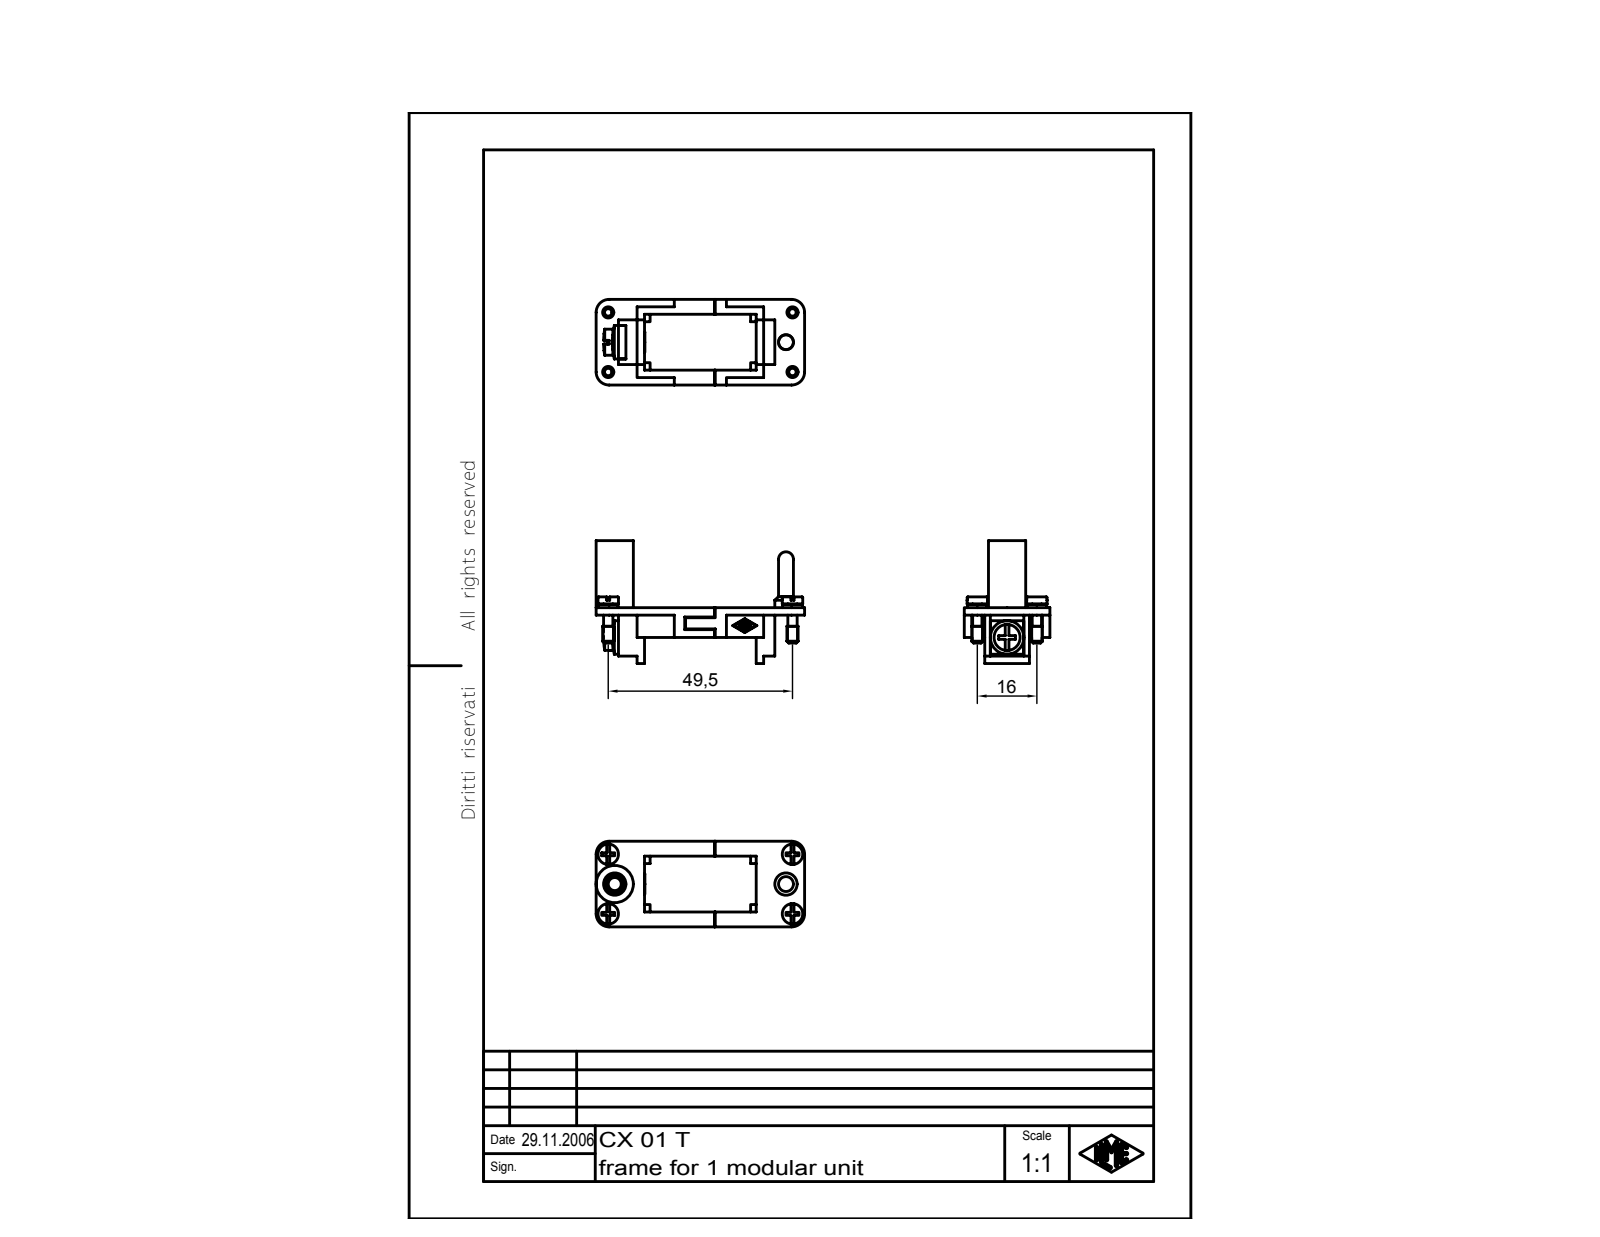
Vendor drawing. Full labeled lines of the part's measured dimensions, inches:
Part name (STEP PRODUCT): CX 01 T
STEP written by: Autodesk Inventor 7 (AUTOMOTIVE_DESIGN)
Units: inches
Bodies: 4 solids, 332 faces (182 planar, 62 cylindrical, 88 other)
Overall size (bounding box): 2.205 × 1.299 × 0.906
Volume: 0.388 in³ · Surface area: 10.89 in²
Round holes (diameter × count): ⌀0.157 ×2, ⌀0.138 ×1, ⌀0.236 ×1
Round bosses / shafts (diameter × count): ⌀0.217 ×2, ⌀0.209 ×2, ⌀0.157 ×2, ⌀0.118 ×2, ⌀0.098 ×2, ⌀0.394 ×1, ⌀0.354 ×1, ⌀0.276 ×1
Partial cylindrical surfaces — rounded edges, fillets, slot ends (radius × count): R0.004 ×14, R0.138 ×4
Main face-to-face distances: 0.079, 0.748, 0.197, 0.157, 0.059, 0.315, 0.827, 0.118, 0.591, 0.138
Hole centre spacings: 1.811
